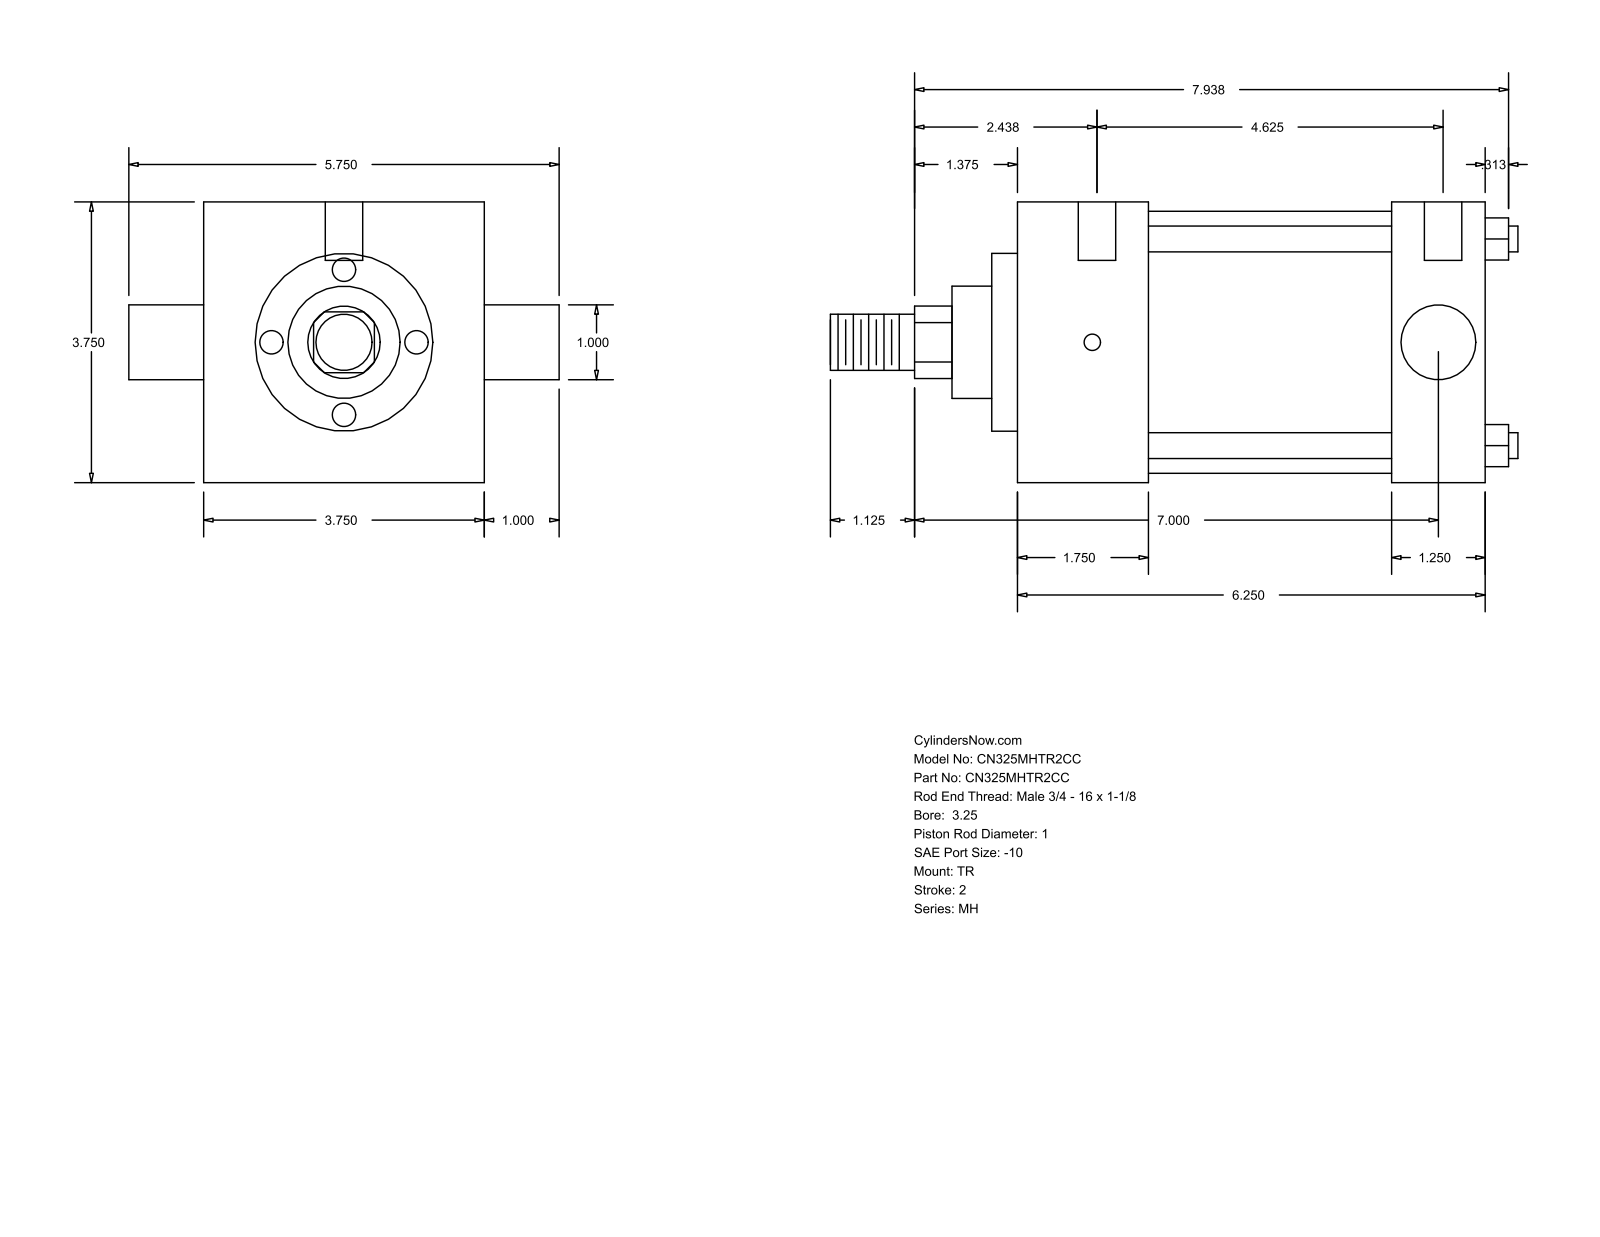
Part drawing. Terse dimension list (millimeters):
name: MH_TR__0325_1
written by: GSSL Pune (CONFIG_CONTROL_DESIGN)
unit: mm
bodies: 0 solids, 86 faces (61 planar, 25 cylindrical, 0 other)
size: 233.36 × 146.05 × 95.25
holes: 3× ⌀5.56, 2× ⌀12.7
bosses: 4× ⌀8.76, 2× ⌀25.4, 1× ⌀88.9, 1× ⌀60.33, 1× ⌀38.1, 1× ⌀19.05
rounds: 1× R12.29
face distances: 95.24, 158.76, 44.46, 127.01, 82.55, 114.3, 31.75, 8.73, 53.19, 135.74
hole spacings: 1.58, 4.76, 117.48, 119.06, 122.24, 123.82
